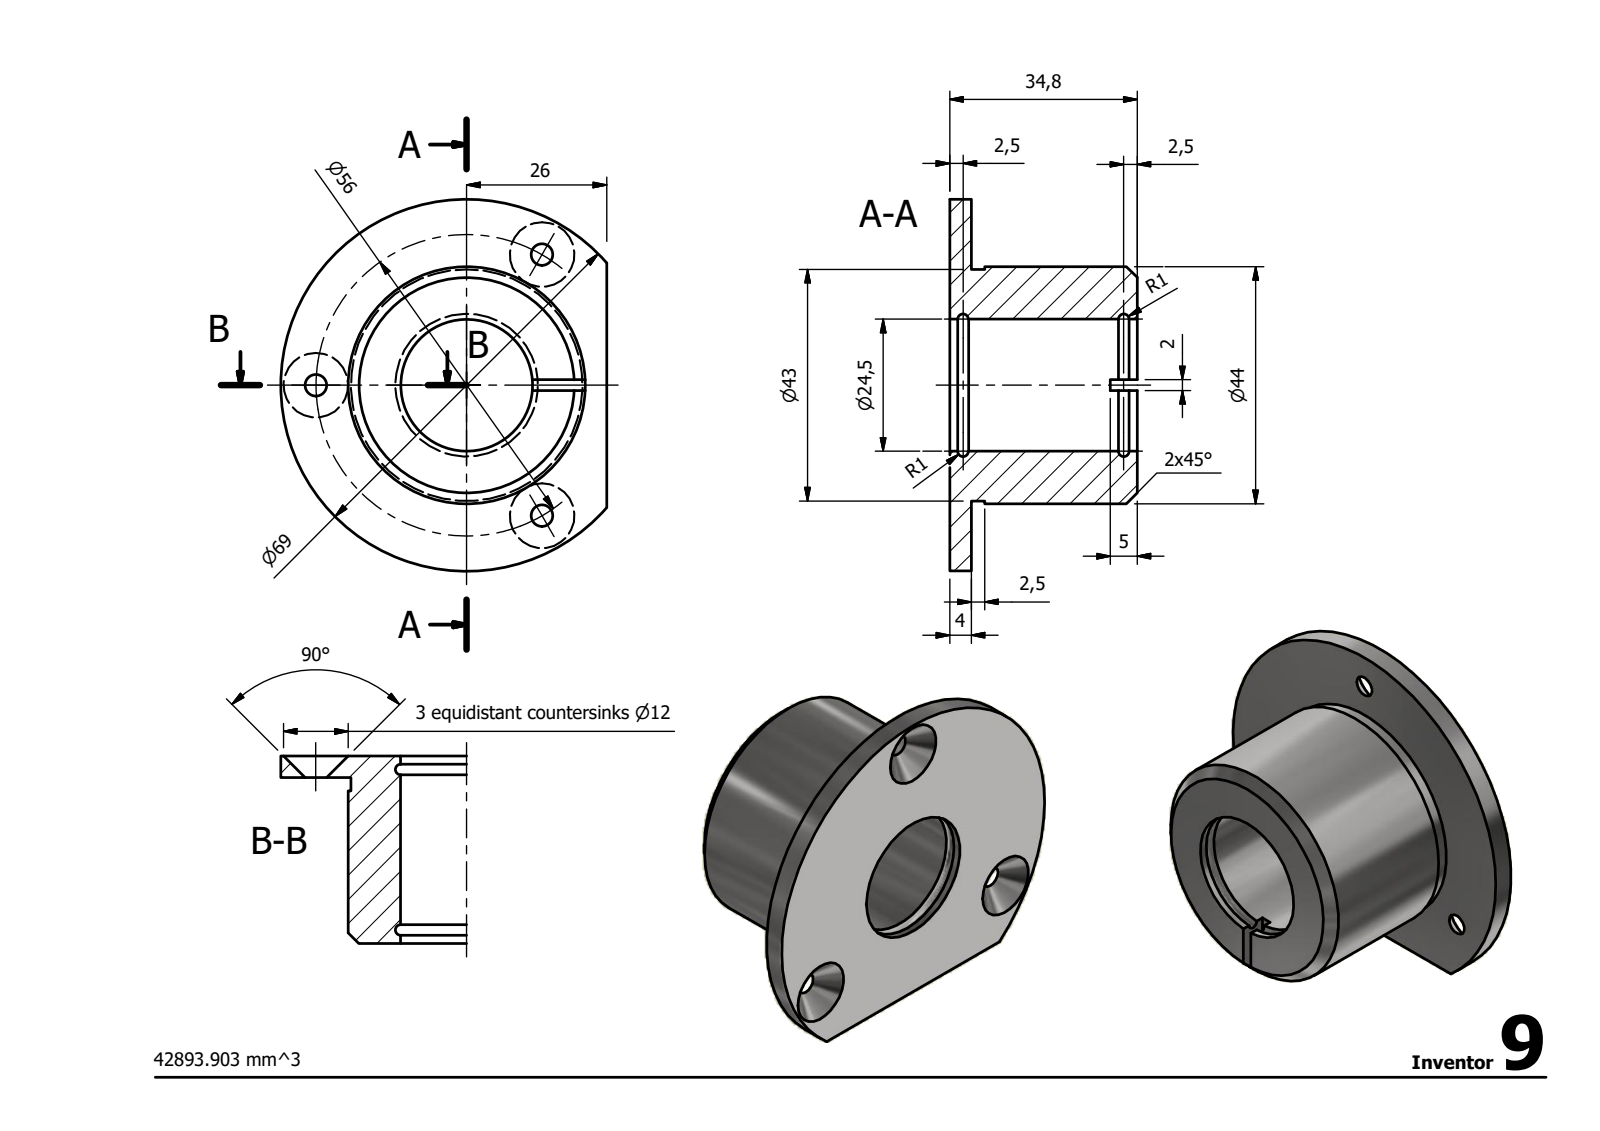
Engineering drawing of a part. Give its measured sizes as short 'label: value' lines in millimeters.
written by: Autodesk Inventor 2014 (AUTOMOTIVE_DESIGN)
unit: mm
bodies: 1 solid, 20 faces (8 planar, 6 cylindrical, 6 other)
size: 69 × 60.5 × 34.8
volume: 42 894 mm³; area: 14 077 mm²
holes: 1× ⌀24.5
bosses: 1× ⌀44, 1× ⌀43
rounds: 1× R34.5
face distances: 4, 30.8, 34.8, 28.3, 2.5, 6.5, 2, 5, 23.3, 25.8
